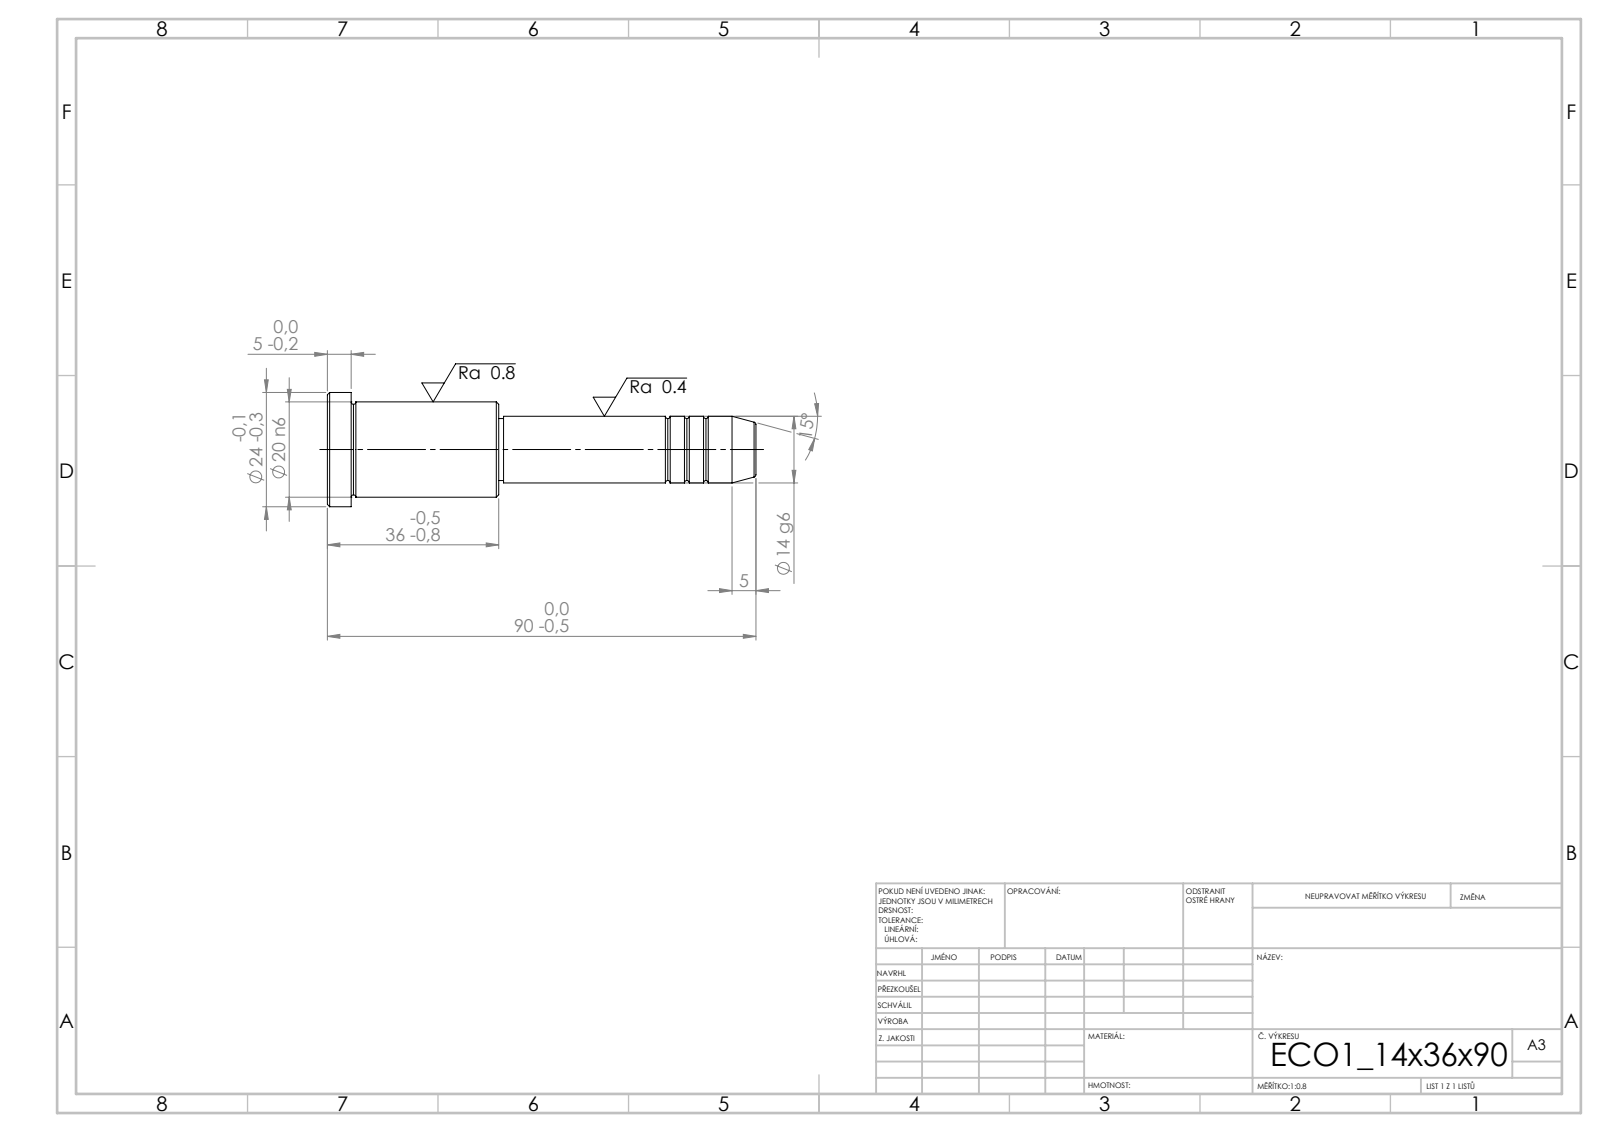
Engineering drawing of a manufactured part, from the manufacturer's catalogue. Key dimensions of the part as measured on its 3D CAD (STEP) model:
STEP written by: SolidWorks 2019 (CONFIG_CONTROL_DESIGN)
Units: millimetres
Bodies: 1 solid, 43 faces (5 planar, 14 cylindrical, 24 other)
Overall size (bounding box): 90 × 24 × 24
Volume: 20 062 mm³ · Surface area: 5 630 mm²
Round bosses / shafts (diameter × count): ⌀24 ×1, ⌀20 ×1, ⌀14 ×1, ⌀13 ×1
Main face-to-face distances: 36, 31, 5, 54, 85, 90, 53, 1, 32, 37
